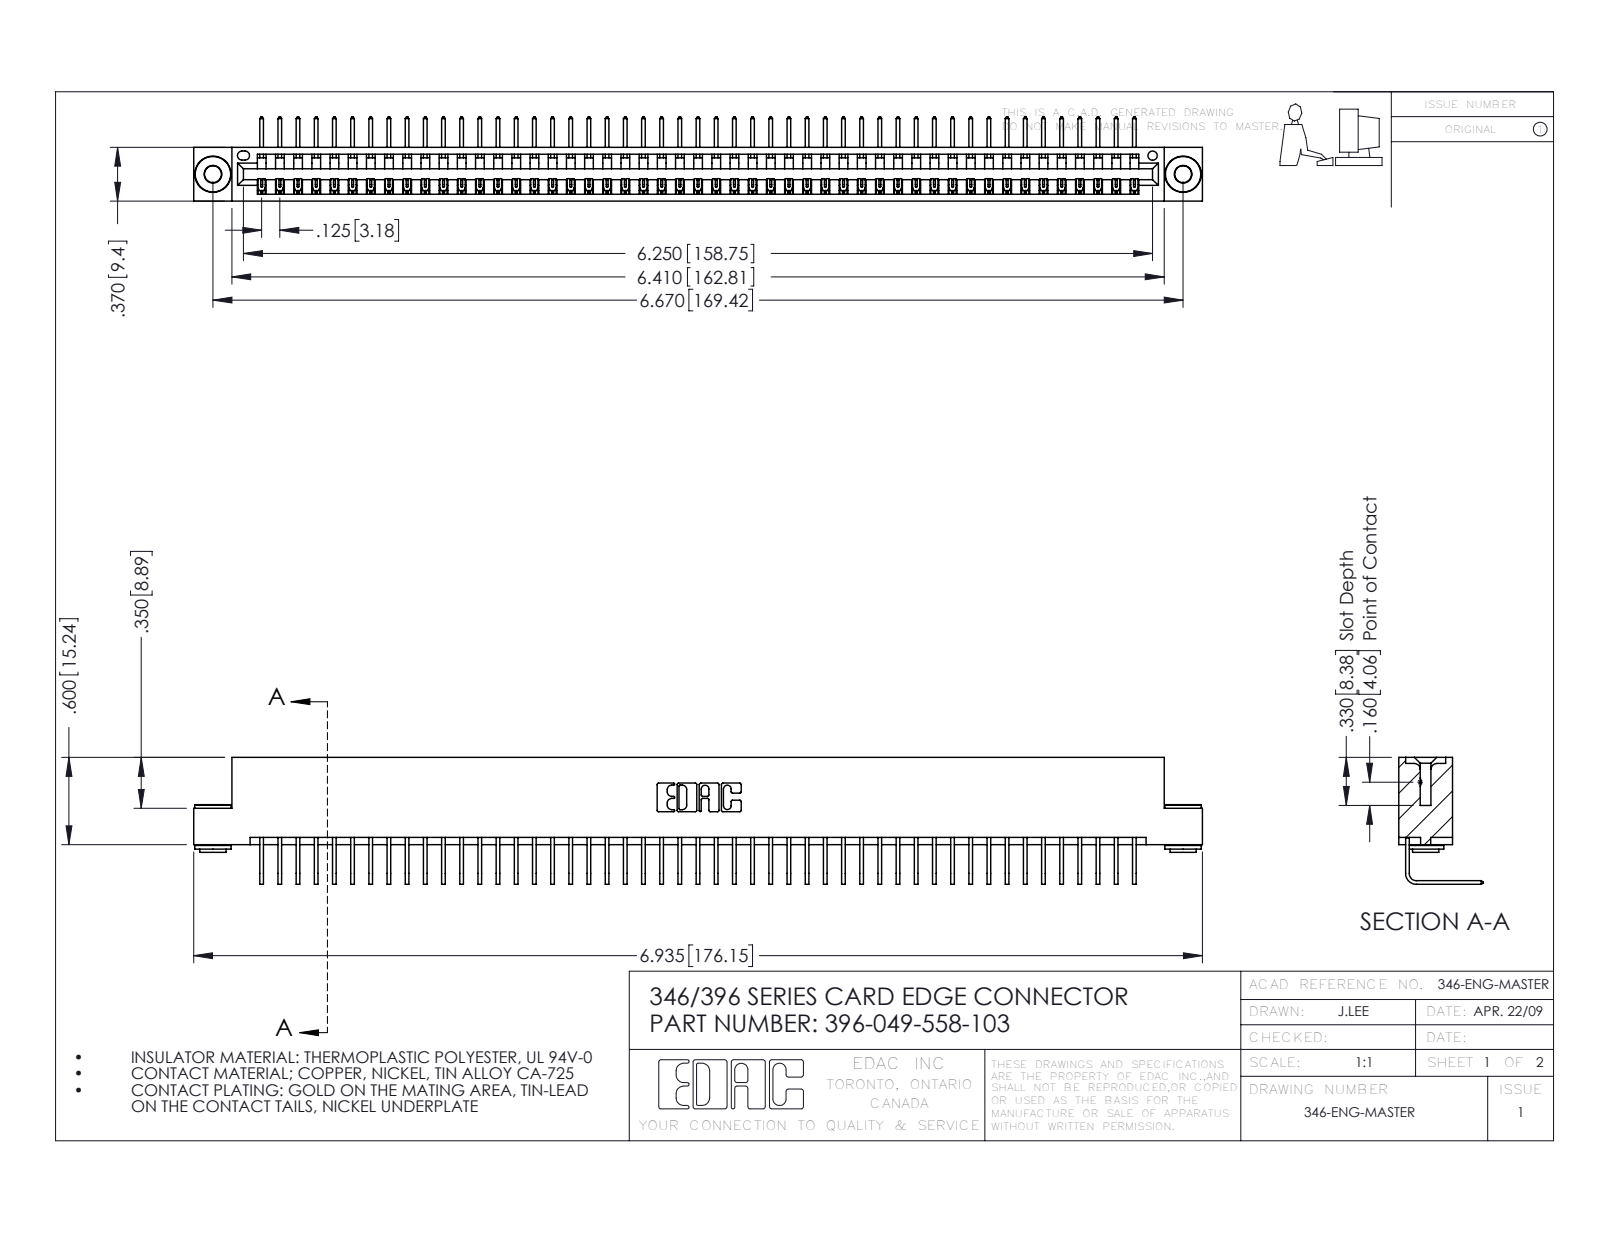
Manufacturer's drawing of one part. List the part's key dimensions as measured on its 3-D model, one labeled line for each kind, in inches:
Part name (STEP PRODUCT): 396-049-558-103; 346 Part_Flush Mounting Lugs - 0.156 Dia-TH; 345-250-002_345-250-002-102; 345-292-001_558 Tail - 2
STEP written by: SolidWorks 2016 (CONFIG_CONTROL_DESIGN)
Units: inches
Bodies: 52 solids, 3100 faces (2144 planar, 948 cylindrical, 8 other)
Overall size (bounding box): 6.935 × 0.873 × 0.58
Volume: 1.043 in³ · Surface area: 35.08 in²
Round holes (diameter × count): ⌀0.116 ×2, ⌀0.156 ×2, ⌀0.064 ×1
Round bosses / shafts (diameter × count): ⌀0.25 ×2, ⌀0.18 ×2, ⌀0.136 ×2
Partial cylindrical surfaces — rounded edges, fillets, slot ends (radius × count): R0.006 ×98, R0.01 ×22, R0.007 ×6, R0.031 ×6, R0.026 ×3, R0.031 ×2, R0.04 ×2, R0.014 ×1
Main face-to-face distances: 0.322, 0.048, 0.37, 0.25, 0.025, 0.298, 0.072, 0.148, 0.222, 0.1
Hole centre spacings: 0.246, 6.461, 6.67
